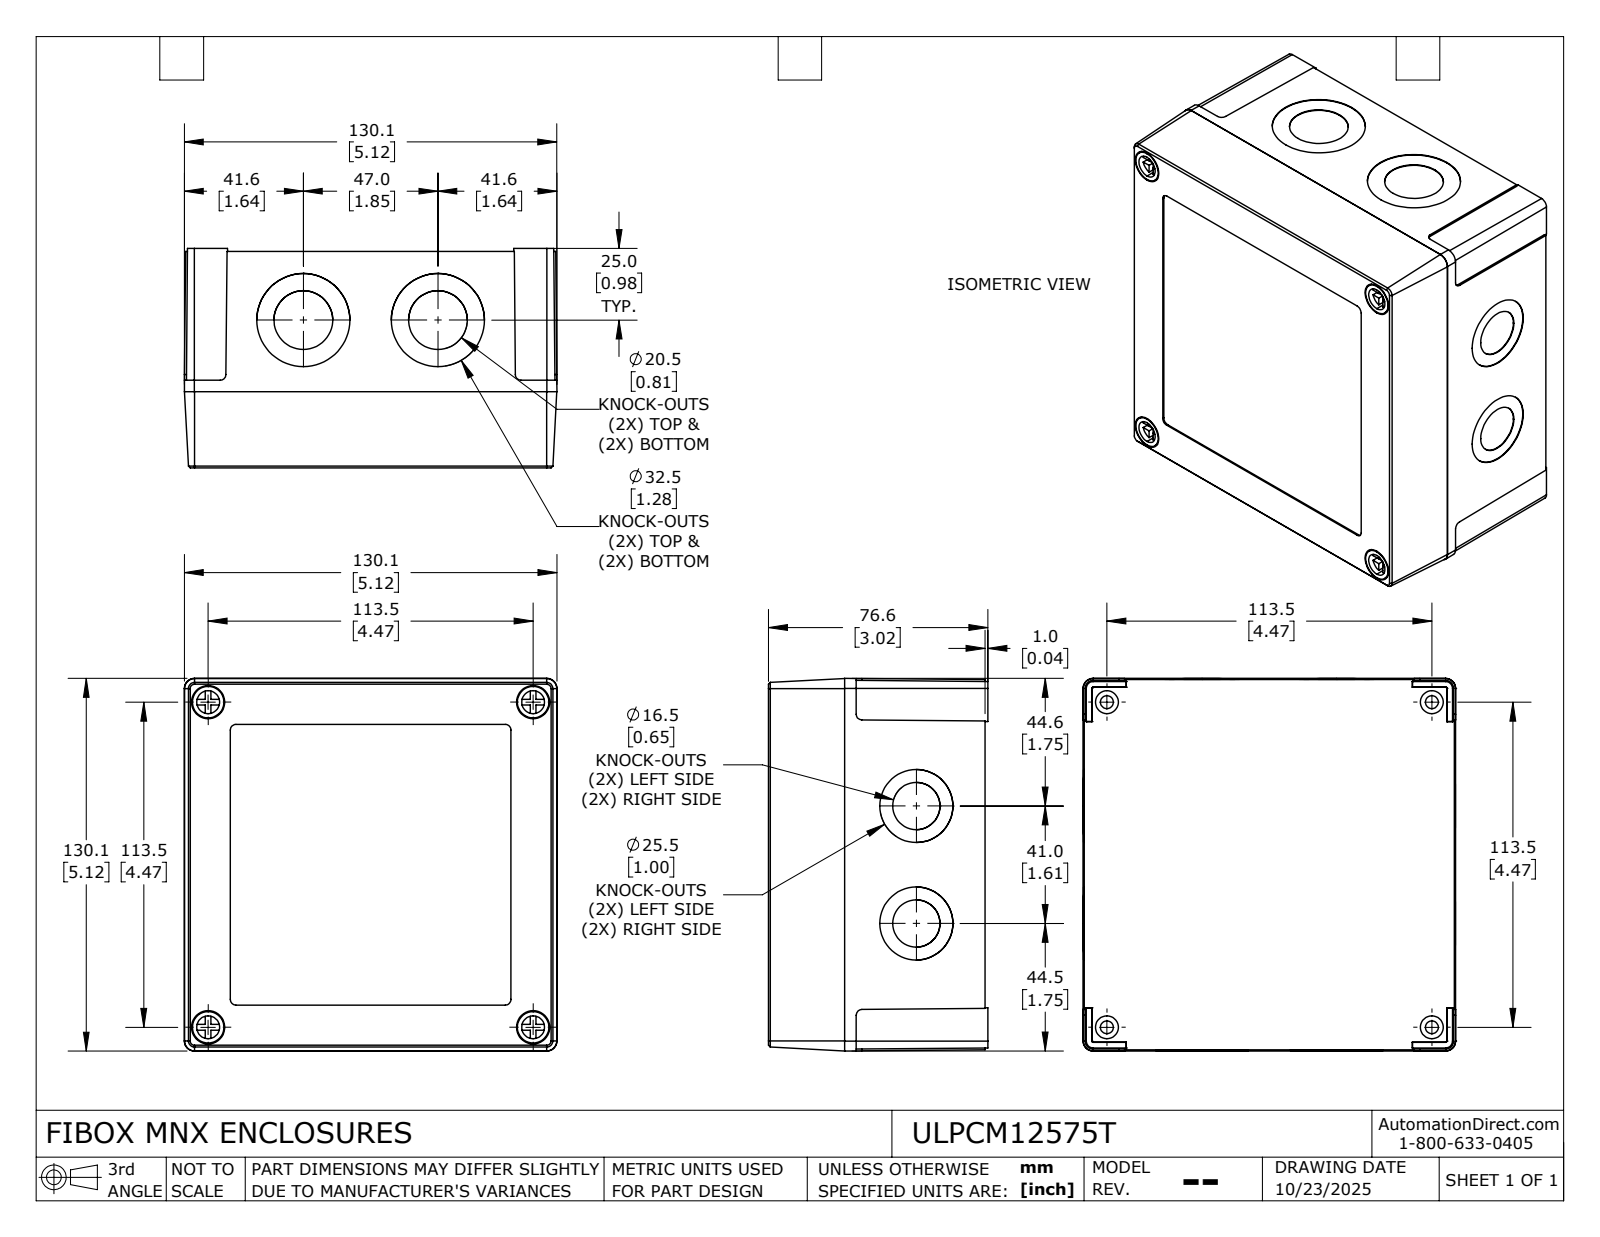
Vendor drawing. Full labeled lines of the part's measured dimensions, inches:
Part name (STEP PRODUCT): ULPCM12575T_Default
STEP written by: SolidWorks 2024 (CONFIG_CONTROL_DESIGN)
Units: inches
Bodies: 6 solids, 522 faces (298 planar, 184 cylindrical, 40 other)
Overall size (bounding box): 5.122 × 5.122 × 3.016
Volume: 15.37 in³ · Surface area: 239.4 in²
Round holes (diameter × count): ⌀0.126 ×8, ⌀0.157 ×8, ⌀0.177 ×4, ⌀0.315 ×4, ⌀0.457 ×4, ⌀0.65 ×4, ⌀0.807 ×4, ⌀1.004 ×4, ⌀1.28 ×4
Round bosses / shafts (diameter × count): ⌀0.315 ×8, ⌀0.098 ×8, ⌀0.433 ×4, ⌀0.283 ×4
Partial cylindrical surfaces — rounded edges, fillets, slot ends (radius × count): R0.079 ×8, R0.056 ×6, R0.021 ×4, R0.197 ×4, R0.023 ×2
Main face-to-face distances: 0.165, 2.878, 0.118, 2.76, 0.079, 2.839, 2.957, 2.858, 0.098, 0.02
Hole centre spacings: 2.281, 4.587, 0.888, 1.476, 1.796, 2.506, 3.543, 3.7
